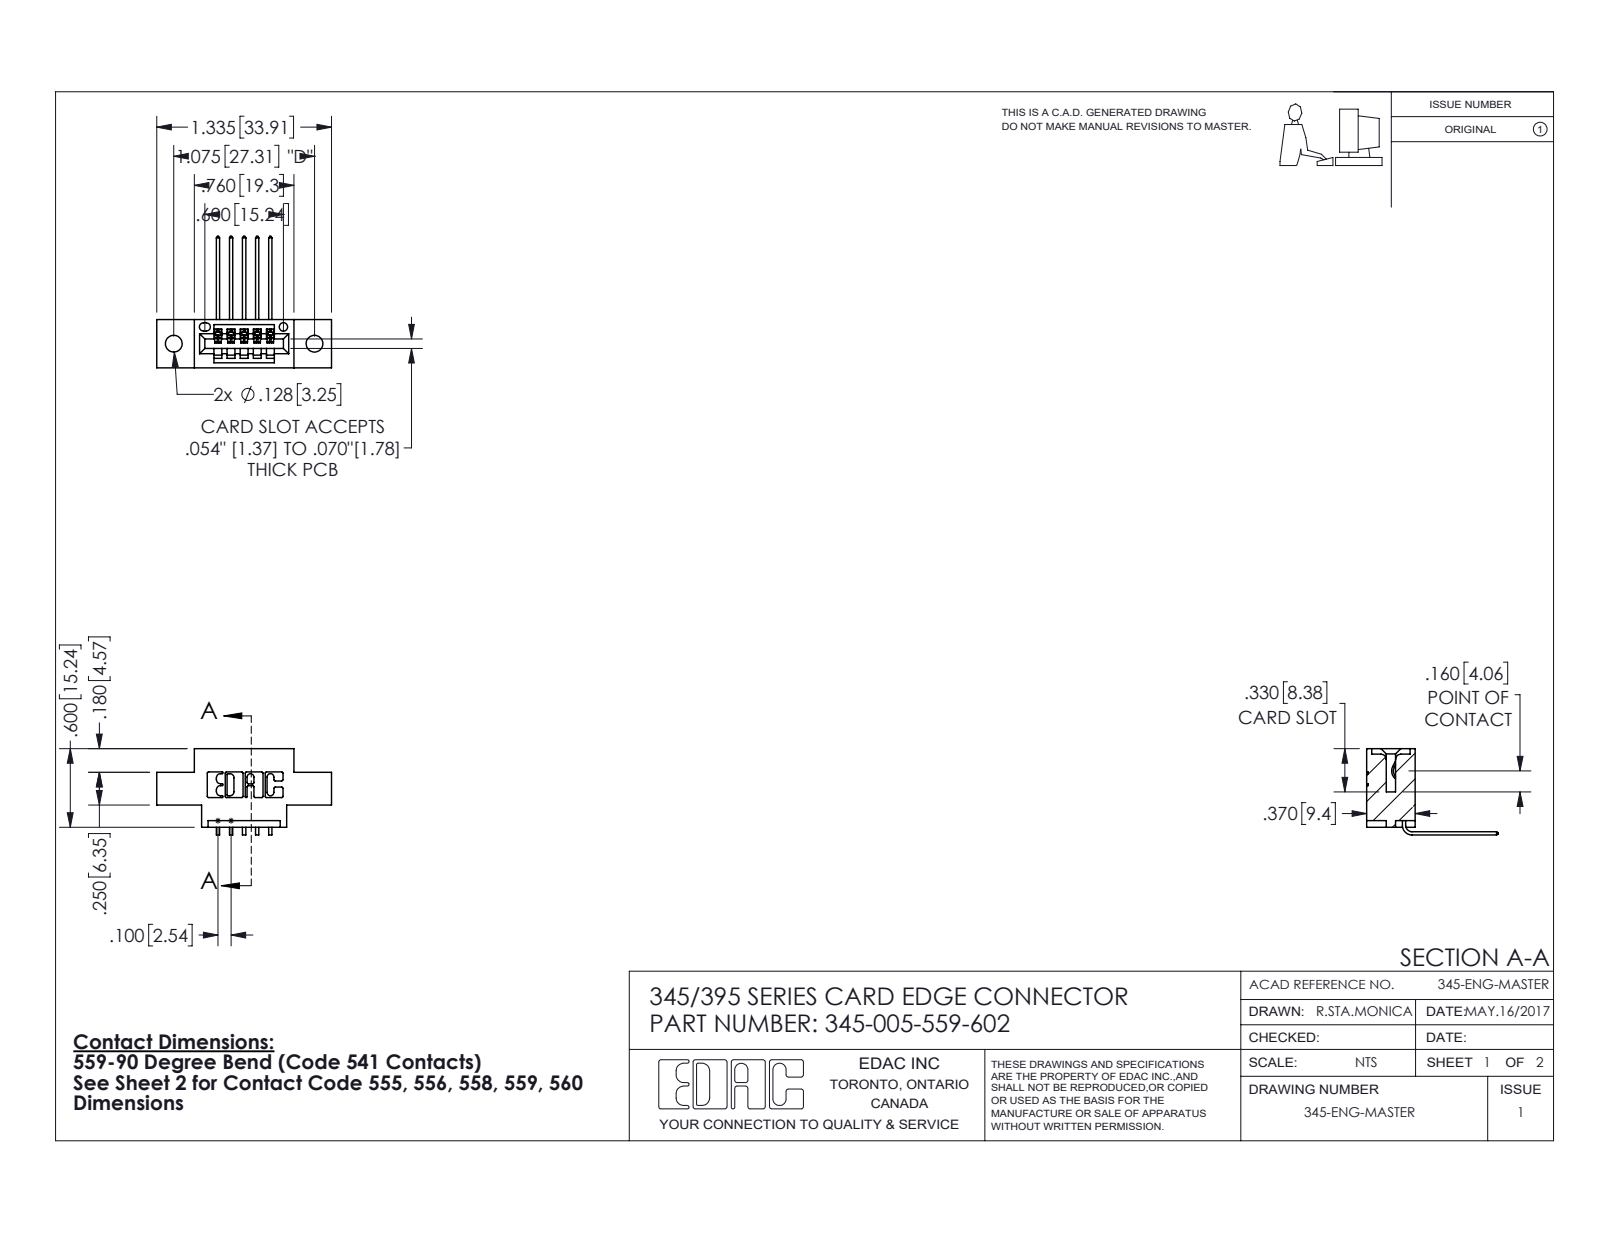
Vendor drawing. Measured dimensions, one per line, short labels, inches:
name: 345-292-001_558 559 Tail - 1; 345-005-559-602; 345 Part_0.170 Offset - 0.128 Dia
written by: SolidWorks 2016 (CONFIG_CONTROL_DESIGN)
unit: in
bodies: 6 solids, 430 faces (294 planar, 136 cylindrical, 0 other)
size: 1.335 × 1.005 × 0.659
volume: 0.17 in³; area: 4.883 in²
holes: 2× ⌀0.128, 1× ⌀0.064
rounds: 22× R0.01, 10× R0.006, 6× R0.007, 6× R0.031, 3× R0.026, 2× R0.031, 2× R0.04, 1× R0.014
face distances: 0.37, 0.2, 0.1, 0.072, 0.298, 0.25, 0.025, 0.06, 0.098, 0.272
hole spacings: 0.27, 0.847, 1.075
